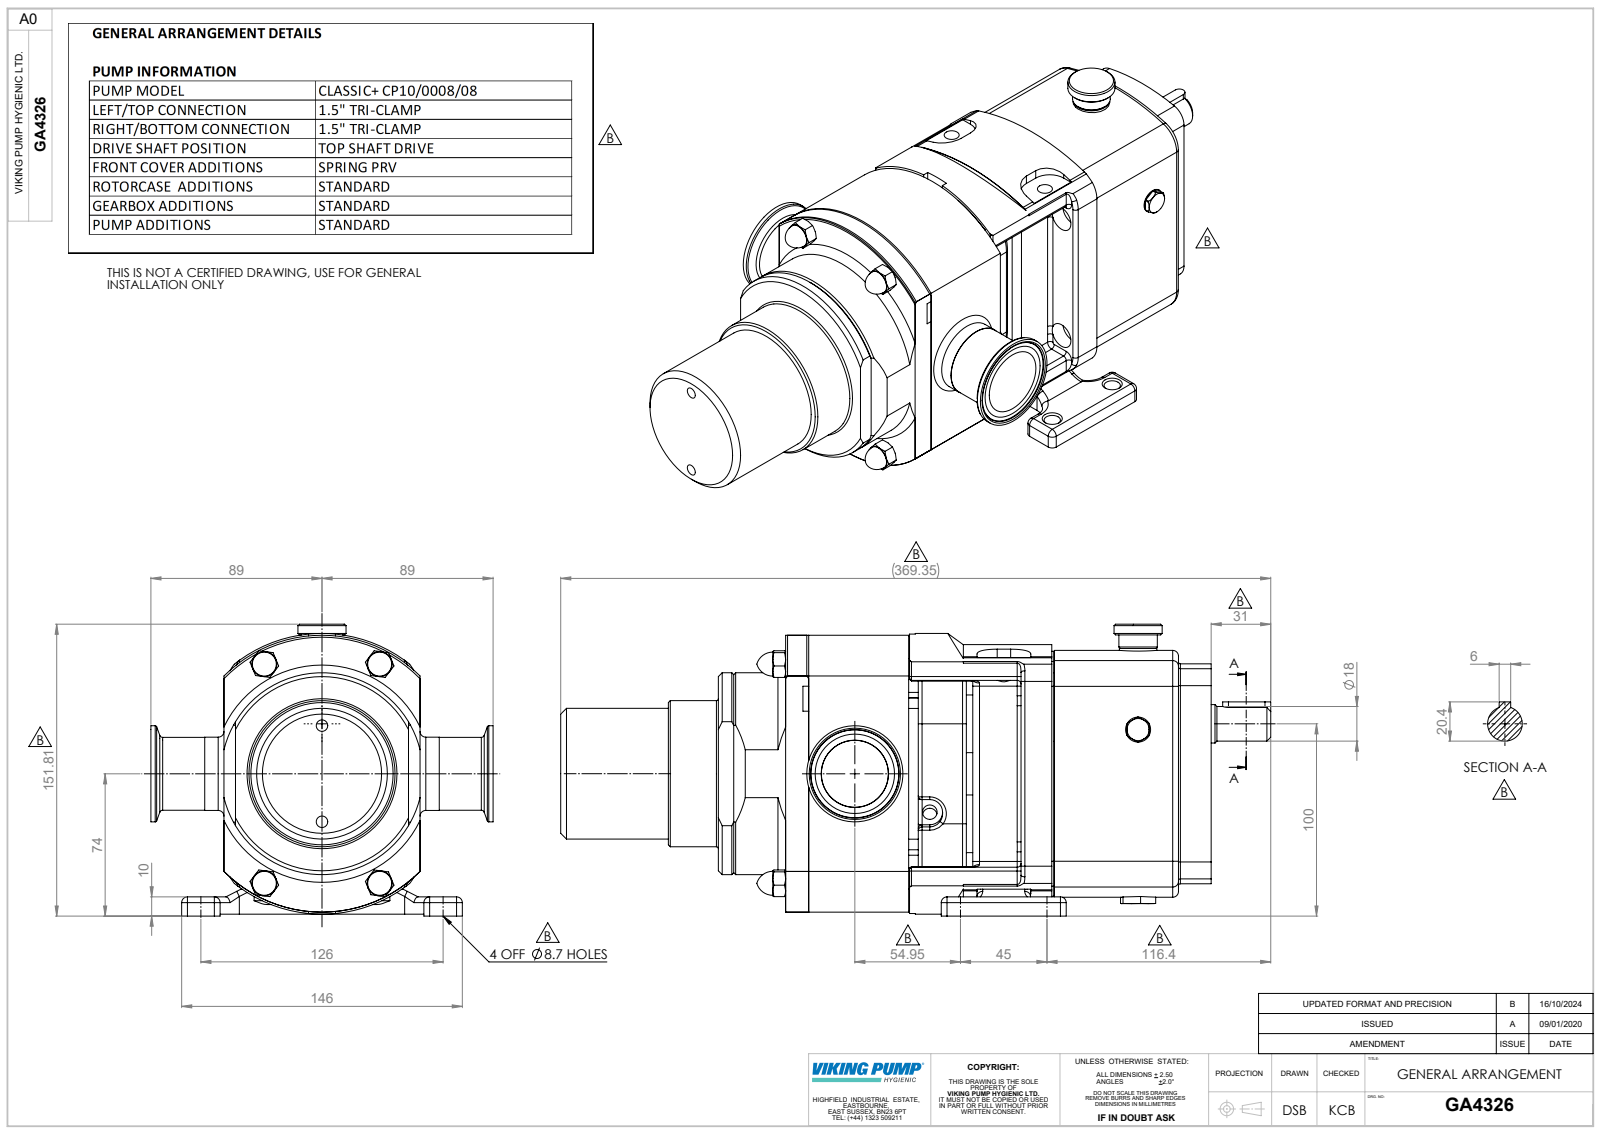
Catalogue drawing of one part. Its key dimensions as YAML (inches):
part_name: "Copy of CP10-0008-08 H T^GA4326; Copy of MP-CP10 SPRING PRV^GA4326; Copy of Z94-5121-22 - 1.5 INCH^GA4326; GA4326"
step_written_by: "SolidWorks 2023 (AUTOMOTIVE_DESIGN)"
units: inches
bodies: {solids: 4, faces: 724, planar: 240, cylindrical: 232, other: 252}
overall_size: [14.541, 7.008, 5.977]
volume: 197.5
surface_area: 387.7
round_holes:
  - {diameter: 0.343, count: 4}
  - {diameter: 0.551, count: 4}
  - {diameter: 0.236, count: 2}
  - {diameter: 0.3, count: 2}
  - {diameter: 0.315, count: 2}
  - {diameter: 0.887, count: 1}
  - {diameter: 1.372, count: 1}
  - {diameter: 1.378, count: 1}
round_bosses_or_shafts:
  - {diameter: 1.181, count: 2}
  - {diameter: 4.134, count: 1}
  - {diameter: 2.992, count: 1}
  - {diameter: 2.677, count: 1}
  - {diameter: 1.969, count: 1}
  - {diameter: 1.5, count: 1}
  - {diameter: 1.492, count: 1}
  - {diameter: 0.985, count: 1}
partial_cylinders:
  - {radius: 0.079, count: 30}
  - {radius: 0.118, count: 26}
  - {radius: 0.531, count: 12}
  - {radius: 0.413, count: 8}
  - {radius: 0.138, count: 6}
  - {radius: 0.217, count: 4}
  - {radius: 0.236, count: 4}
  - {radius: 0.354, count: 4}
face_to_face_distances: [0.472, 0.197, 4.016, 8.242, 8.715, 3.228, 4.882, 5.079, 3.819, 0.197]
hole_center_spacings: [1.414, 3.959, 1.6, 1.601, 1.772, 2.905, 2.909, 2.992]
